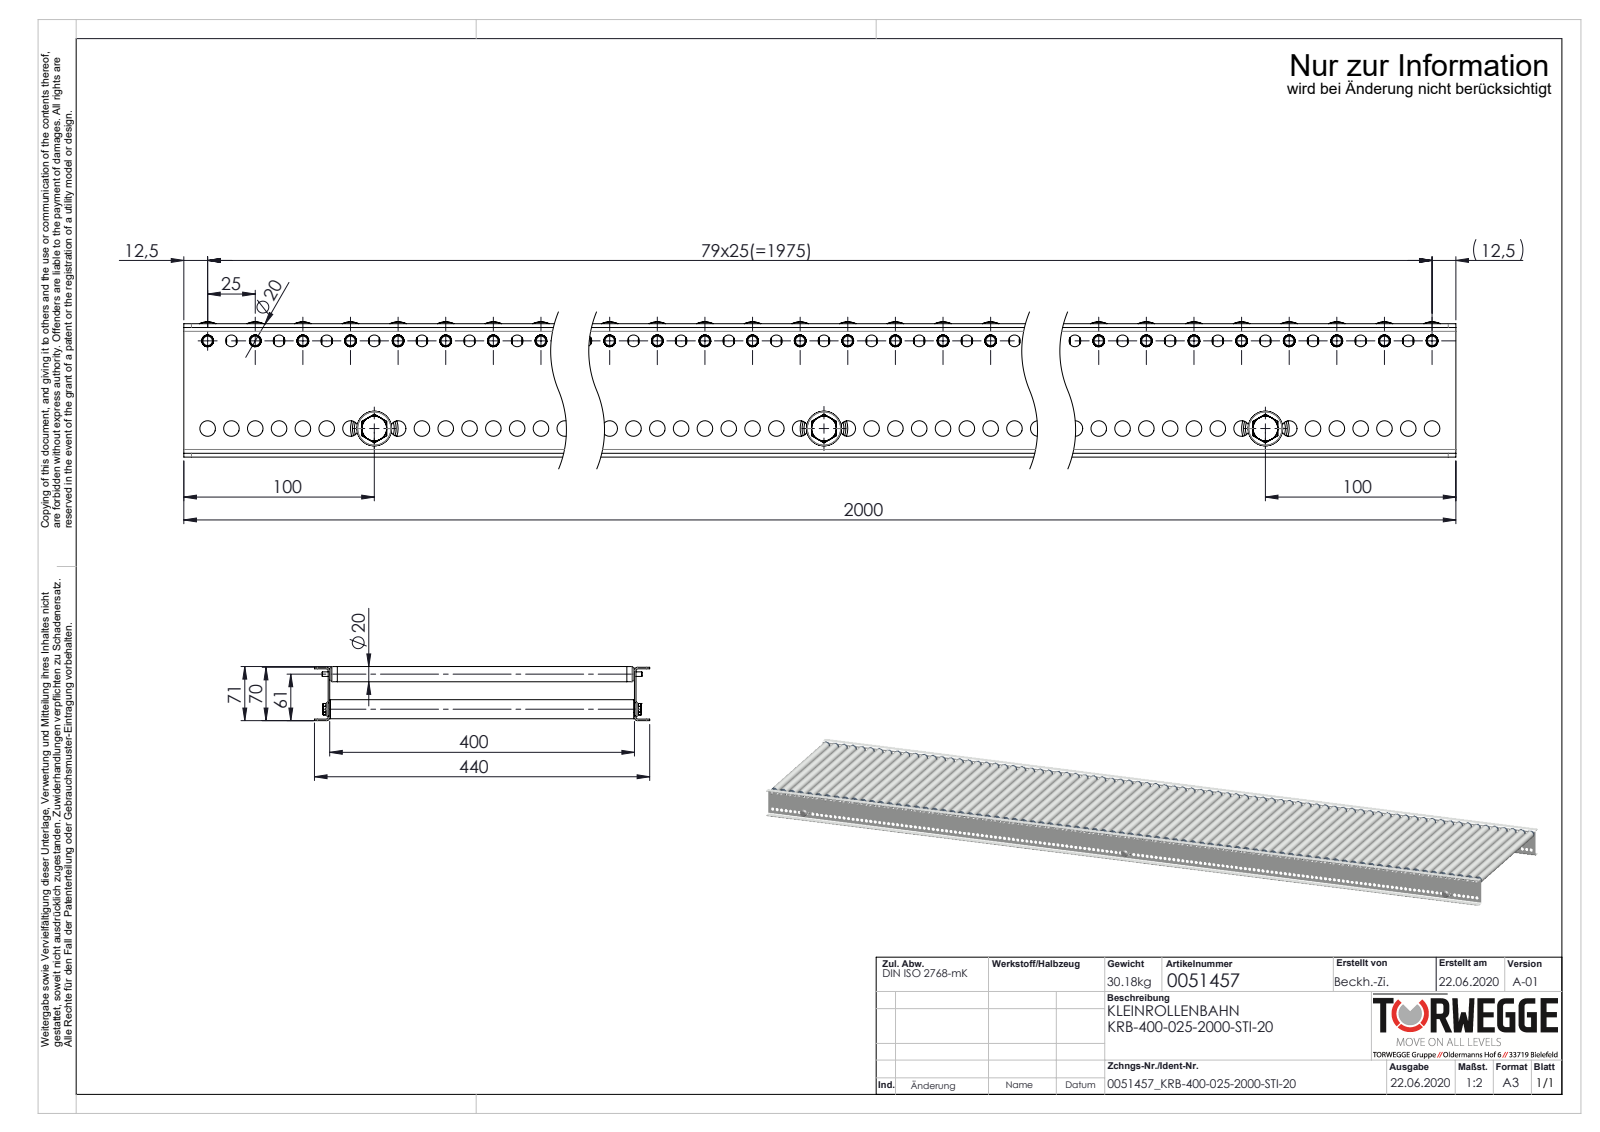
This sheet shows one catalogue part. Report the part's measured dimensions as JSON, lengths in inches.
{"part_name": "KUT50-20x1,5-STI-A6_FA-EL=KFG_S100910_KUT50-20x1-STI-A6-FA-EL=400; Traversen_KFG_L400; S100993_Tragrollenrohr-Ø20x1STI_KFG_L=380; 0051457 (+4 more)", "step_written_by": "SolidWorks 2020 (AUTOMOTIVE_DESIGN)", "units": "inches", "bodies": {"solids": 177, "faces": 15746, "planar": 5122, "cylindrical": 5988, "other": 4636}, "overall_size": [78.74, 17.323, 2.795], "volume_in3": 229.1, "surface_area_in2": 8988, "round_holes": [[0.244, 159], [0.323, 159], [0.24, 80], [0.559, 80], [0.677, 80], [0.709, 80], [0.268, 3], [0.827, 3]], "round_bosses_or_shafts": [[0.787, 80], [0.783, 80], [0.713, 80], [0.701, 80], [0.65, 80], [0.236, 80], [0.984, 3], [0.315, 3]], "partial_cylinders_radius": [[0.159, 80], [0.157, 8], [0.079, 4]], "face_to_face_distances": [0.079, 15.827, 2.677, 15.748, 15.906, 2.756, 2.598, 15.433, 0.709, 1.181], "hole_center_spacings": [0.492, 0.984, 1.476, 1.969, 2.461, 2.953, 3.445, 3.937]}
